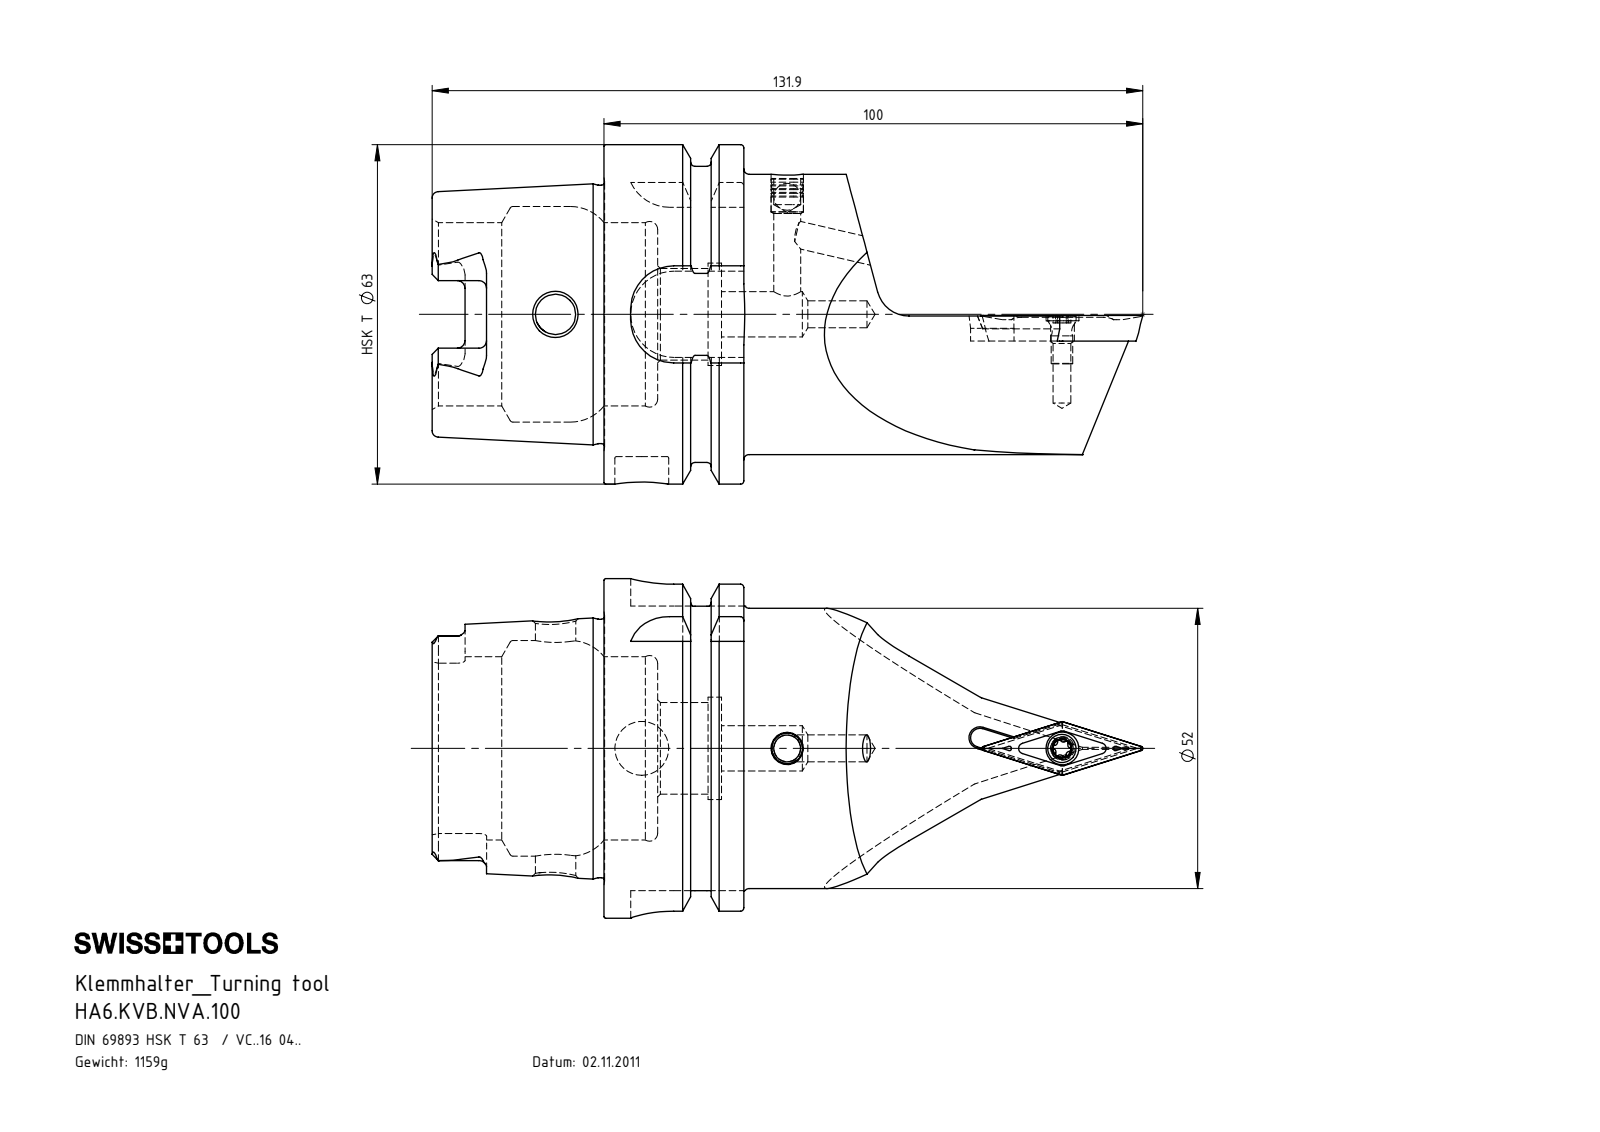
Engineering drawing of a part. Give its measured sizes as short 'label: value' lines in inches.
name: HA6.KVB.NVA.100; KVT_MB_600_060; WCB-ER2.001.009_A; VCMT160404 (+1 more)
written by: SolidWorks 2011 (CONFIG_CONTROL_DESIGN)
unit: in
bodies: 5 solids, 309 faces (84 planar, 86 cylindrical, 139 other)
size: 5.194 × 2.48 × 2.48
volume: 8.98 in³; area: 47.84 in²
holes: 3× ⌀0.197, 1× ⌀0.13, 1× ⌀0.173, 1× ⌀0.24, 1× ⌀0.295, 1× ⌀0.331, 1× ⌀0.394, 1× ⌀0.669, 1× ⌀0.748, 1× ⌀1.339, 1× ⌀1.575
bosses: 1× ⌀2.48, 1× ⌀2.163, 1× ⌀2.047, 1× ⌀1.887, 1× ⌀0.236, 1× ⌀0.207, 1× ⌀0.157
rounds: 6× R0.013, 6× R0.023, 6× R0.055, 4× R0.315, 2× R0.111, 2× R0.113, 1× R0.069, 1× R0.236
face distances: 1.022, 0.63, 0.392, 1.256, 1.648, 2.278, 2.079, 0.858, 0.467, 0.183
hole spacings: 1.063, 2.007, 2.011, 3.07, 3.074
